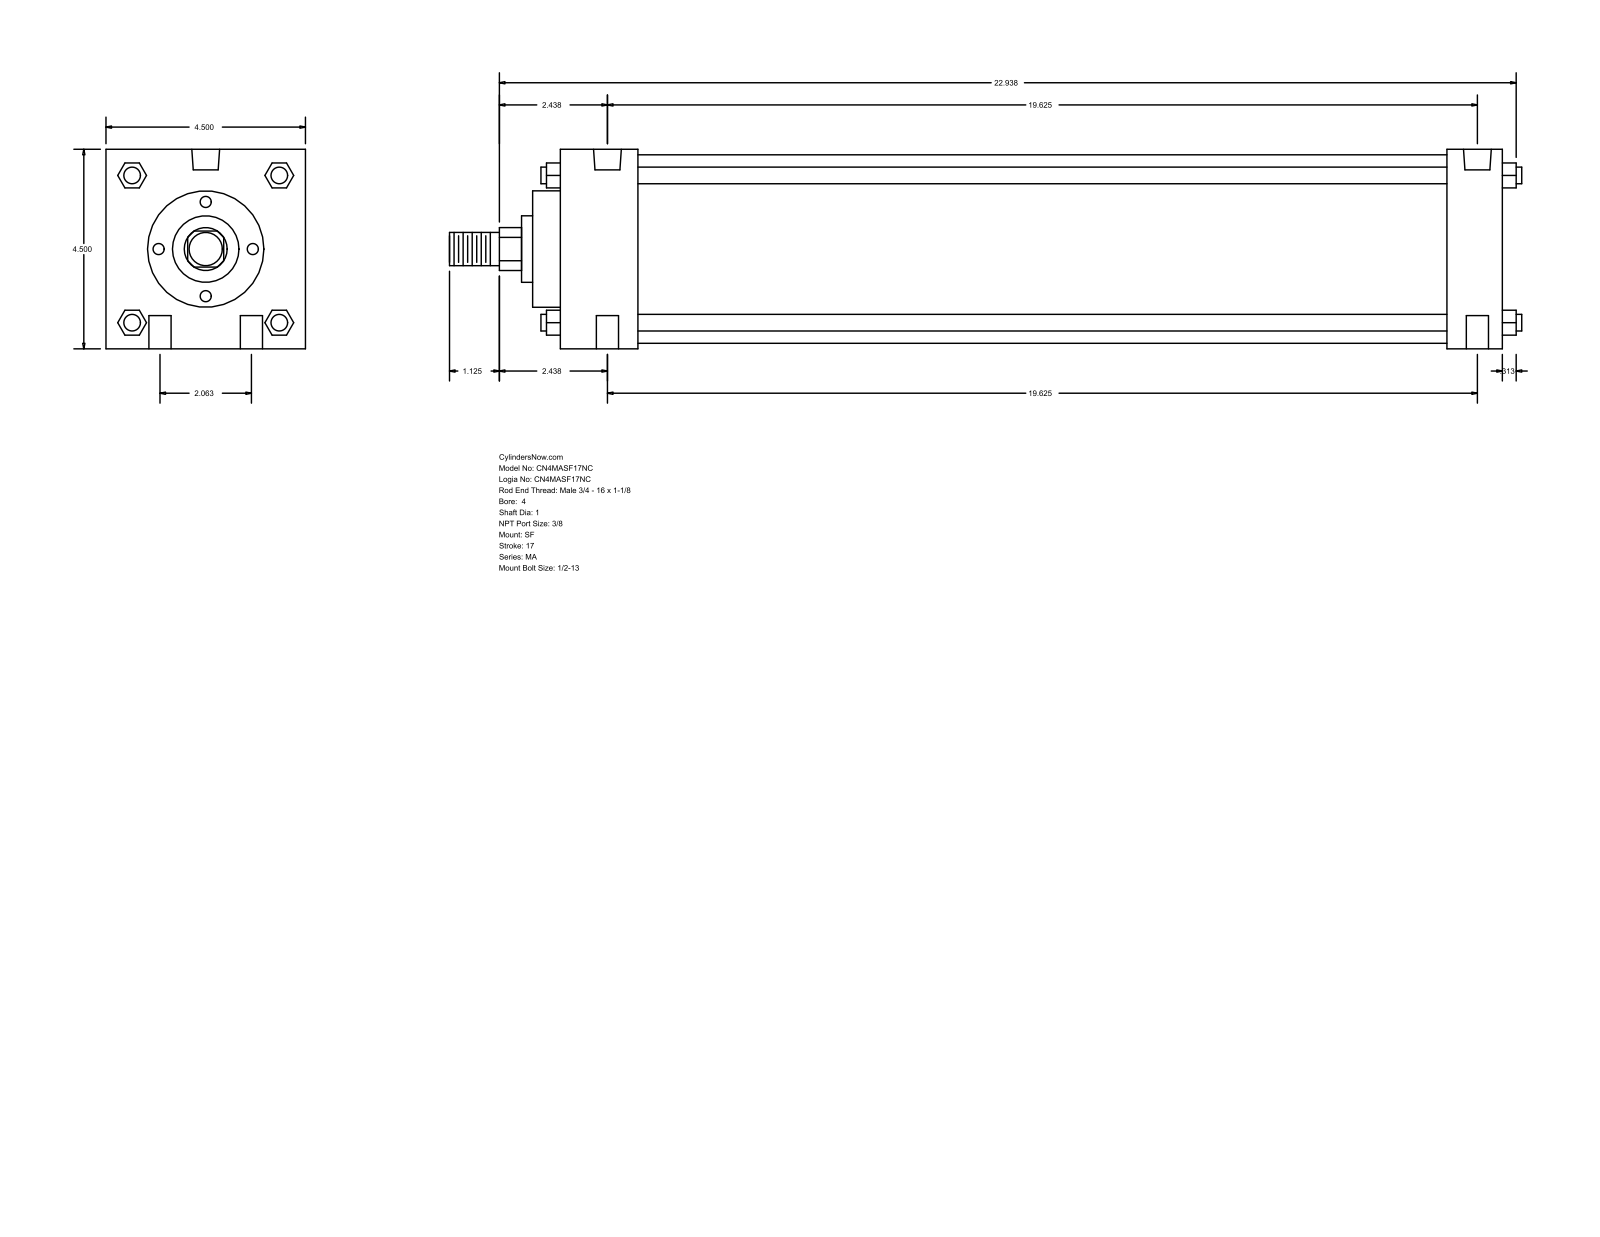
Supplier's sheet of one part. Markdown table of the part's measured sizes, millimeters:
| quantity | value |
| --- | --- |
| part name | MA_SF__0400_1 |
| STEP written by | GSSL Pune (CONFIG_CONTROL_DESIGN) |
| units | millimeters |
| bodies | 0 solids, 126 faces (95 planar, 31 cylindrical, 0 other) |
| overall size | 614.36 × 114.3 × 114.3 |
| round holes (diameter × count) | 12.7 × 4, 11.11 × 2, 15.93 × 2 |
| round bosses / shafts (diameter × count) | 9.53 × 4, 107.95 × 1, 66.67 × 1, 38.1 × 1, 25.4 × 1, 19.05 × 1 |
| partial cylindrical surfaces (radius × count) | 12.29 × 1 |
| main face-to-face distances | 114.3, 539.75, 508, 31.75, 44.46, 463.54, 495.29, 555.62, 15.87, 60.33 |
| hole center spacings | 26.19, 499.17, 498.48, 52.38, 501.22, 488.95 |
